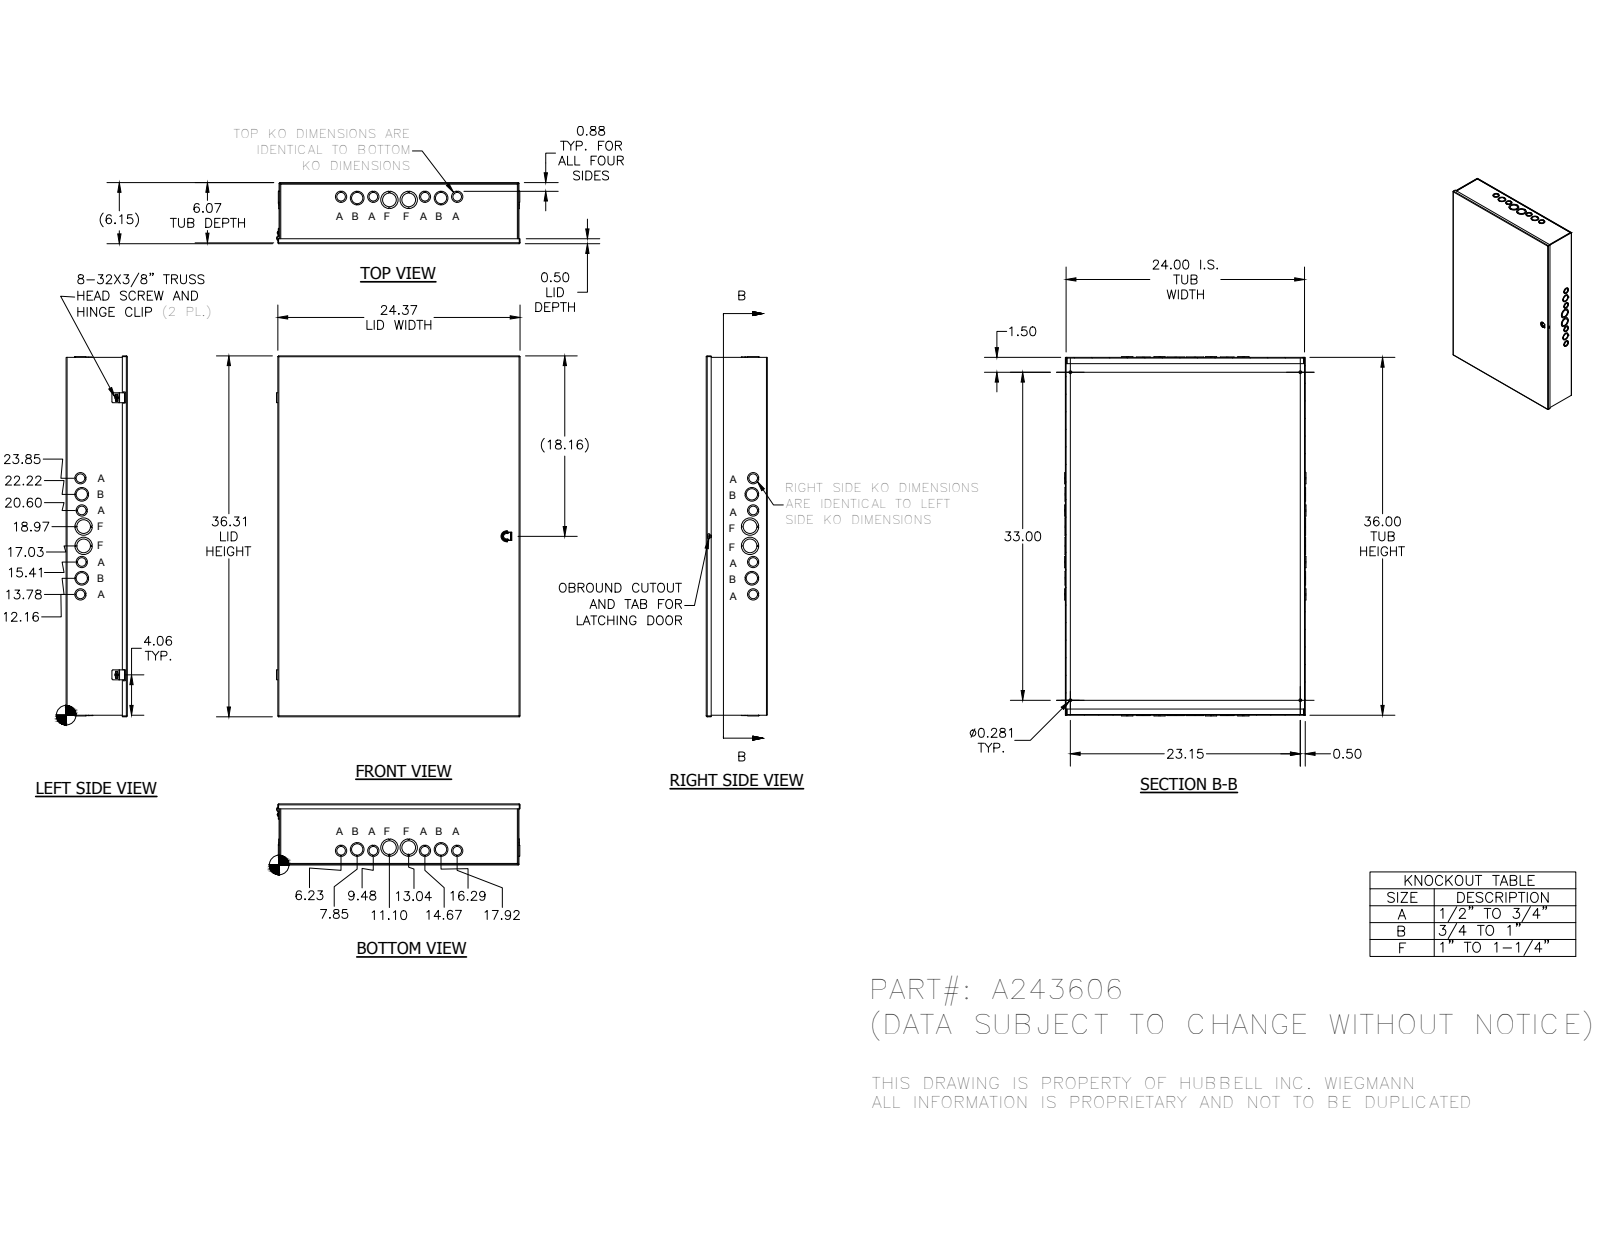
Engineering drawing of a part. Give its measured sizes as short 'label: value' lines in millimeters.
name: A243606BLR; A2406TB; A2436LFA; 31816 (+3 more)
written by: Autodesk Inventor 2014 (AUTOMOTIVE_DESIGN)
unit: mm
bodies: 38 solids, 1287 faces (941 planar, 281 cylindrical, 65 other)
size: 922.31 × 623.39 × 156.21
holes: 14× ⌀28.57, 10× ⌀22.22, 8× ⌀34.92, 4× ⌀7.14, 4× ⌀44.45, 2× ⌀3.56
bosses: 2× ⌀9.75, 2× ⌀4.17
rounds: 12× R0.4, 12× R2.28, 10× R0.79, 10× R1.59, 7× R3.17, 4× R1.78, 4× R2.37, 4× R2.38
face distances: 1.88, 1.57, 154.33, 152.76, 154.64, 156.21, 611.48, 912.52, 609.6, 613.36
hole spacings: 41.39, 41.4, 42.03, 82.55, 82.69, 90.9, 124.07, 131.92
